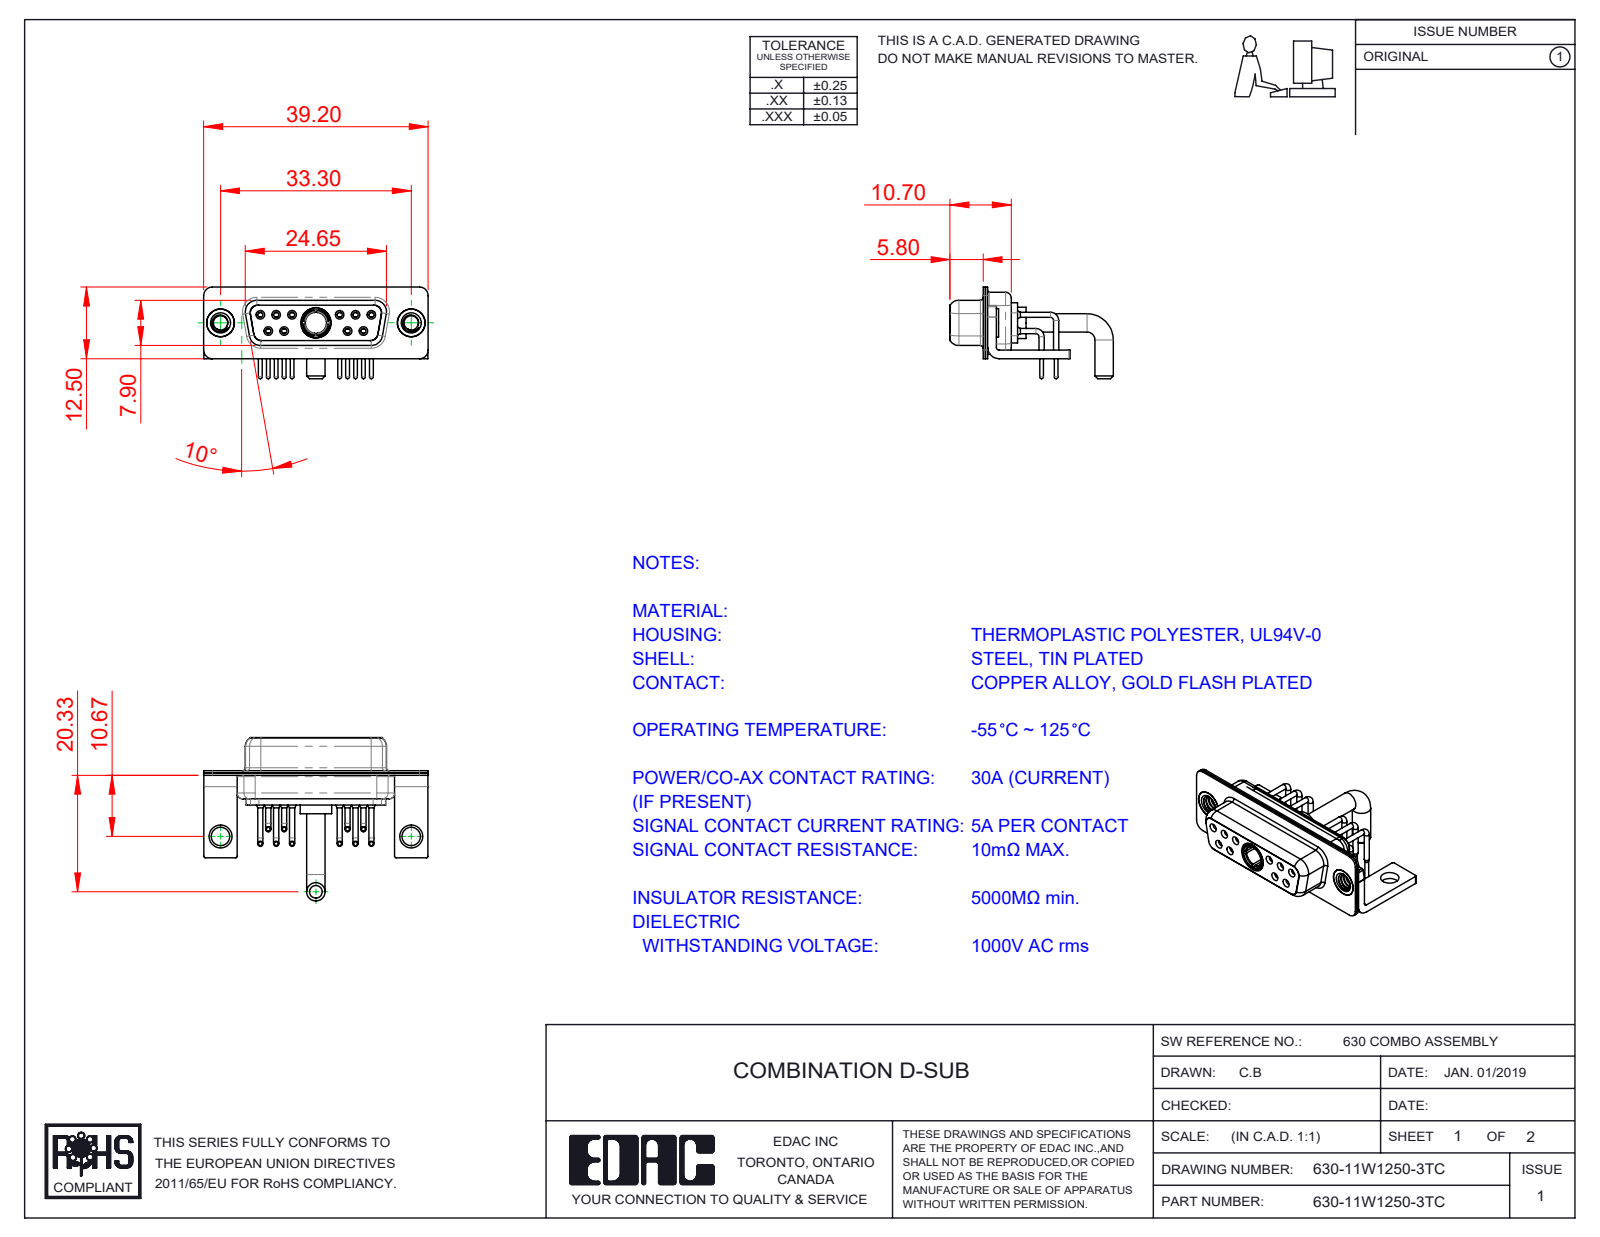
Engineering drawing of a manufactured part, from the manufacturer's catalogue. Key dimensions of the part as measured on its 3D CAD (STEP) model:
Part name (STEP PRODUCT): 630Combo Shell Rear_15 Contacts; 630Combo Threaded Rivet_B; 630Combo Housing_11W1; Power Socket_Ext 30A RA (+5 more)
STEP written by: SolidWorks 2020 (CONFIG_CONTROL_DESIGN)
Units: millimetres
Bodies: 19 solids, 925 faces (266 planar, 410 cylindrical, 249 other)
Overall size (bounding box): 39.2 × 28.53 × 16
Volume: 2 993 mm³ · Surface area: 6 950 mm²
Round holes (diameter × count): ⌀0.9 ×10, ⌀1.1 ×10, ⌀1.5 ×10, ⌀2 ×10, ⌀1.7 ×6, ⌀1.6 ×4, ⌀4.85 ×3, ⌀2.5 ×2, ⌀3.2 ×2, ⌀4 ×2, ⌀4.05 ×2, ⌀3.7 ×1
Round bosses / shafts (diameter × count): ⌀0.9 ×10, ⌀0.65 ×10, ⌀1.6 ×6, ⌀5 ×2, ⌀4.95 ×2, ⌀4.8 ×2, ⌀3.2 ×2, ⌀5.5 ×1
Partial cylindrical surfaces — rounded edges, fillets, slot ends (radius × count): R0.25 ×16, R1.5 ×16, R2 ×13, R1.35 ×12, R1.6 ×8, R0.5 ×5, R0.6 ×4, R0.65 ×4
Main face-to-face distances: 0.4, 0.8, 1.4, 0.45, 8.45, 1.5, 1.8, 8.9, 6.2, 2.3
Hole centre spacings: 3.16, 2.77, 13.85, 11.08, 16.62, 5.03, 5.04, 5.54
